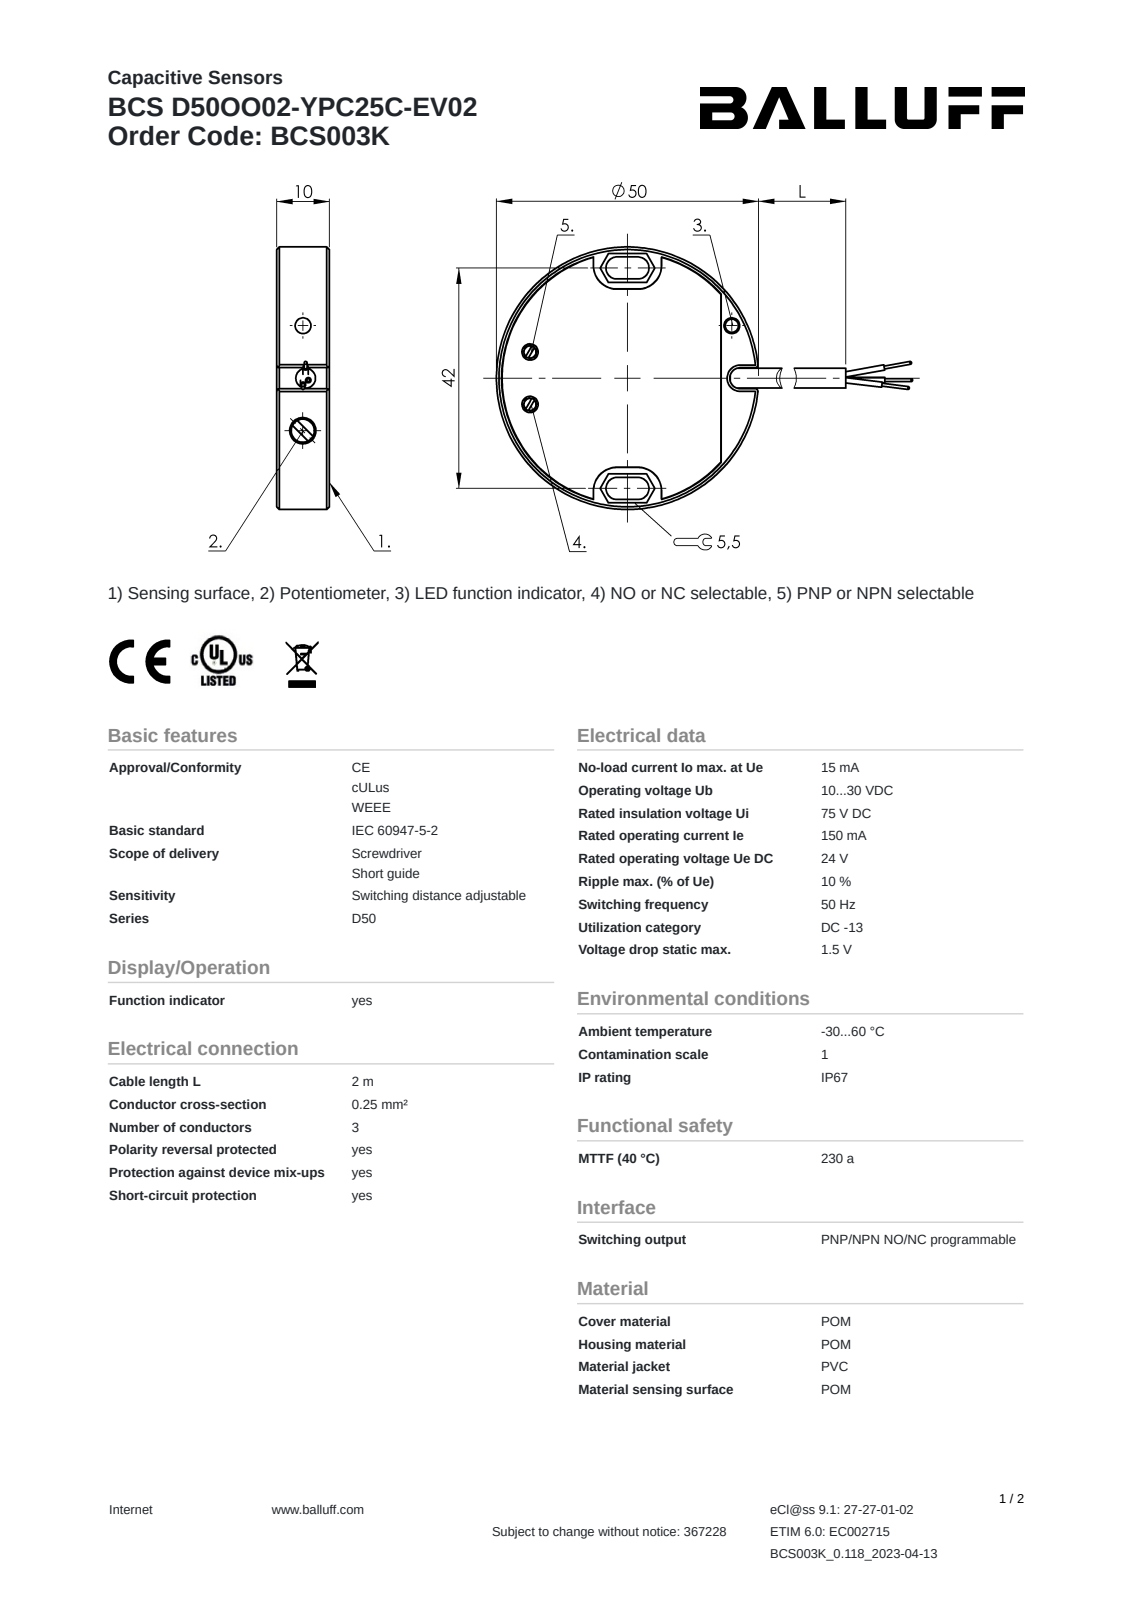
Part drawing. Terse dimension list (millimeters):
name: BCS003K
written by: SolidWorks 2021 (AUTOMOTIVE_DESIGN)
unit: mm
bodies: 1 solid, 183 faces (113 planar, 61 cylindrical, 9 other)
size: 65 × 50 × 10
volume: 18 550 mm³; area: 6 587 mm²
holes: 2× ⌀2.4, 1× ⌀2.5, 1× ⌀3, 1× ⌀4.4, 1× ⌀5, 1× ⌀10.3, 1× ⌀20.7, 1× ⌀30.6
bosses: 2× ⌀2.3, 1× ⌀50, 1× ⌀30, 1× ⌀20.1, 1× ⌀9.8, 1× ⌀3.8
rounds: 8× R4.5, 6× R0.5, 4× R2.1, 2× R2, 1× R24, 1× R24
face distances: 10, 42, 5.5, 9, 21, 3.7, 6.4, 10, 47.5, 36.5
hole spacings: 19.2, 10, 20, 22.3, 38.8, 41.3
